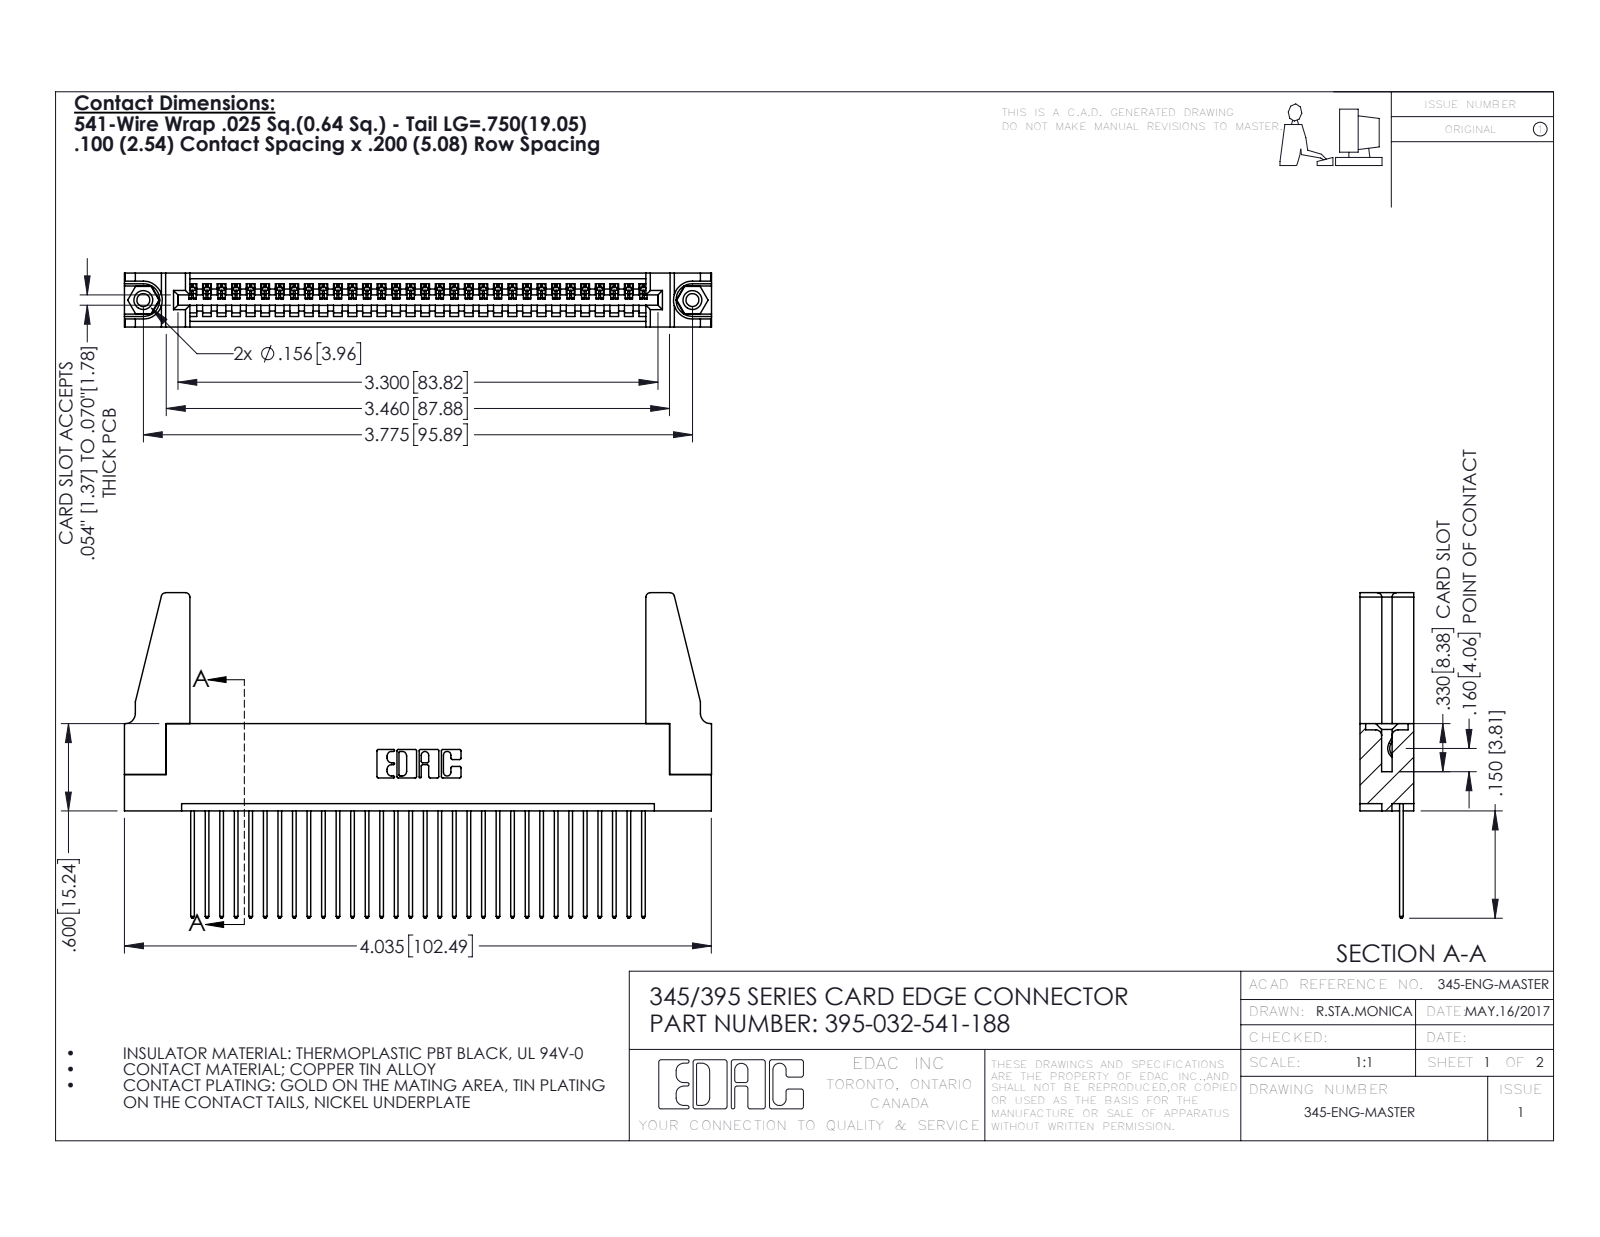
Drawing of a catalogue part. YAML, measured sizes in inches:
part_name: "345-220-078_345-220-088; 345-292-001_345-293-141; 345 Part_Flush Mounting Lugs - 0.156 Dia-TH; 345-250-001_345-250-001-102 (+1 more)"
step_written_by: "SolidWorks 2016 (CONFIG_CONTROL_DESIGN)"
units: inches
bodies: {solids: 37, faces: 2106, planar: 1432, cylindrical: 658, other: 16}
overall_size: [4.036, 2.237, 0.37]
volume: 0.794
surface_area: 25.71
round_holes:
  - {diameter: 0.089, count: 2}
  - {diameter: 0.125, count: 2}
  - {diameter: 0.156, count: 2}
  - {diameter: 0.064, count: 1}
round_bosses_or_shafts:
  - {diameter: 0.155, count: 2}
partial_cylinders:
  - {radius: 0.006, count: 64}
  - {radius: 0.01, count: 64}
  - {radius: 0.01, count: 22}
  - {radius: 0.03, count: 8}
  - {radius: 0.007, count: 6}
  - {radius: 0.031, count: 6}
  - {radius: 0.026, count: 3}
  - {radius: 0.031, count: 2}
face_to_face_distances: [0.072, 0.298, 0.37, 0.2, 0.098, 0.272, 0.025, 0.225, 0.149, 0.072]
hole_center_spacings: [0.27, 3.54, 3.775]
